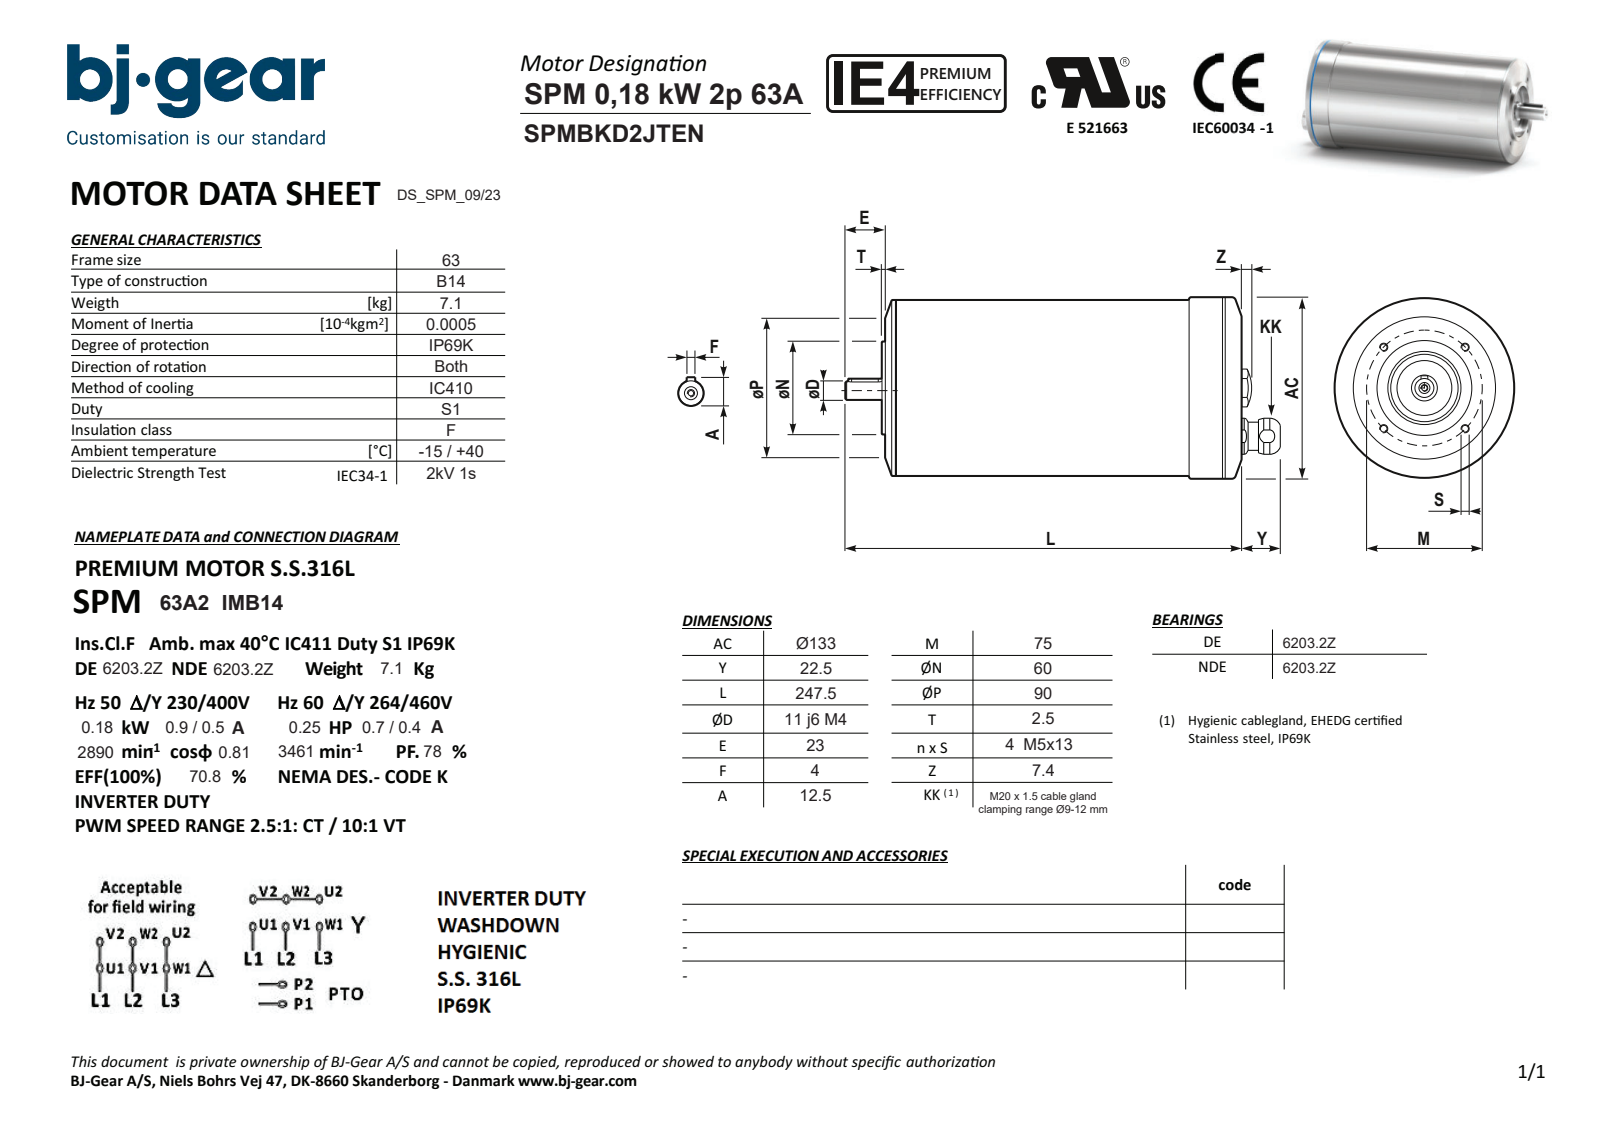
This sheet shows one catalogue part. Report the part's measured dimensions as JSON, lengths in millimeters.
{"part_name": "SPMBKD2JTENN4KSA1-N---NNN", "step_written_by": "Solid Edge (AUTOMOTIVE_DESIGN)", "units": "millimeters", "bodies": {"solids": 1, "faces": 87, "planar": 30, "cylindrical": 32, "other": 25}, "overall_size": [275, 133, 133], "volume_mm3": 2939000, "surface_area_mm2": 120931, "round_holes": [[4.13, 4], [3.24, 1], [4.3, 1], [7, 1], [13.4, 1], [52, 1]], "round_bosses_or_shafts": [[133, 1], [132.98, 1], [129, 1], [128.98, 1], [60, 1], [20, 1], [17, 1], [11, 1]], "partial_cylinders_radius": [[2, 2], [12.8, 1]], "face_to_face_distances": [224.5, 219, 5.5, 2.5, 8, 227, 24, 12, 231, 236.5], "hole_center_spacings": [37.5, 53.04, 27.55, 66.08, 75.01, 34]}
